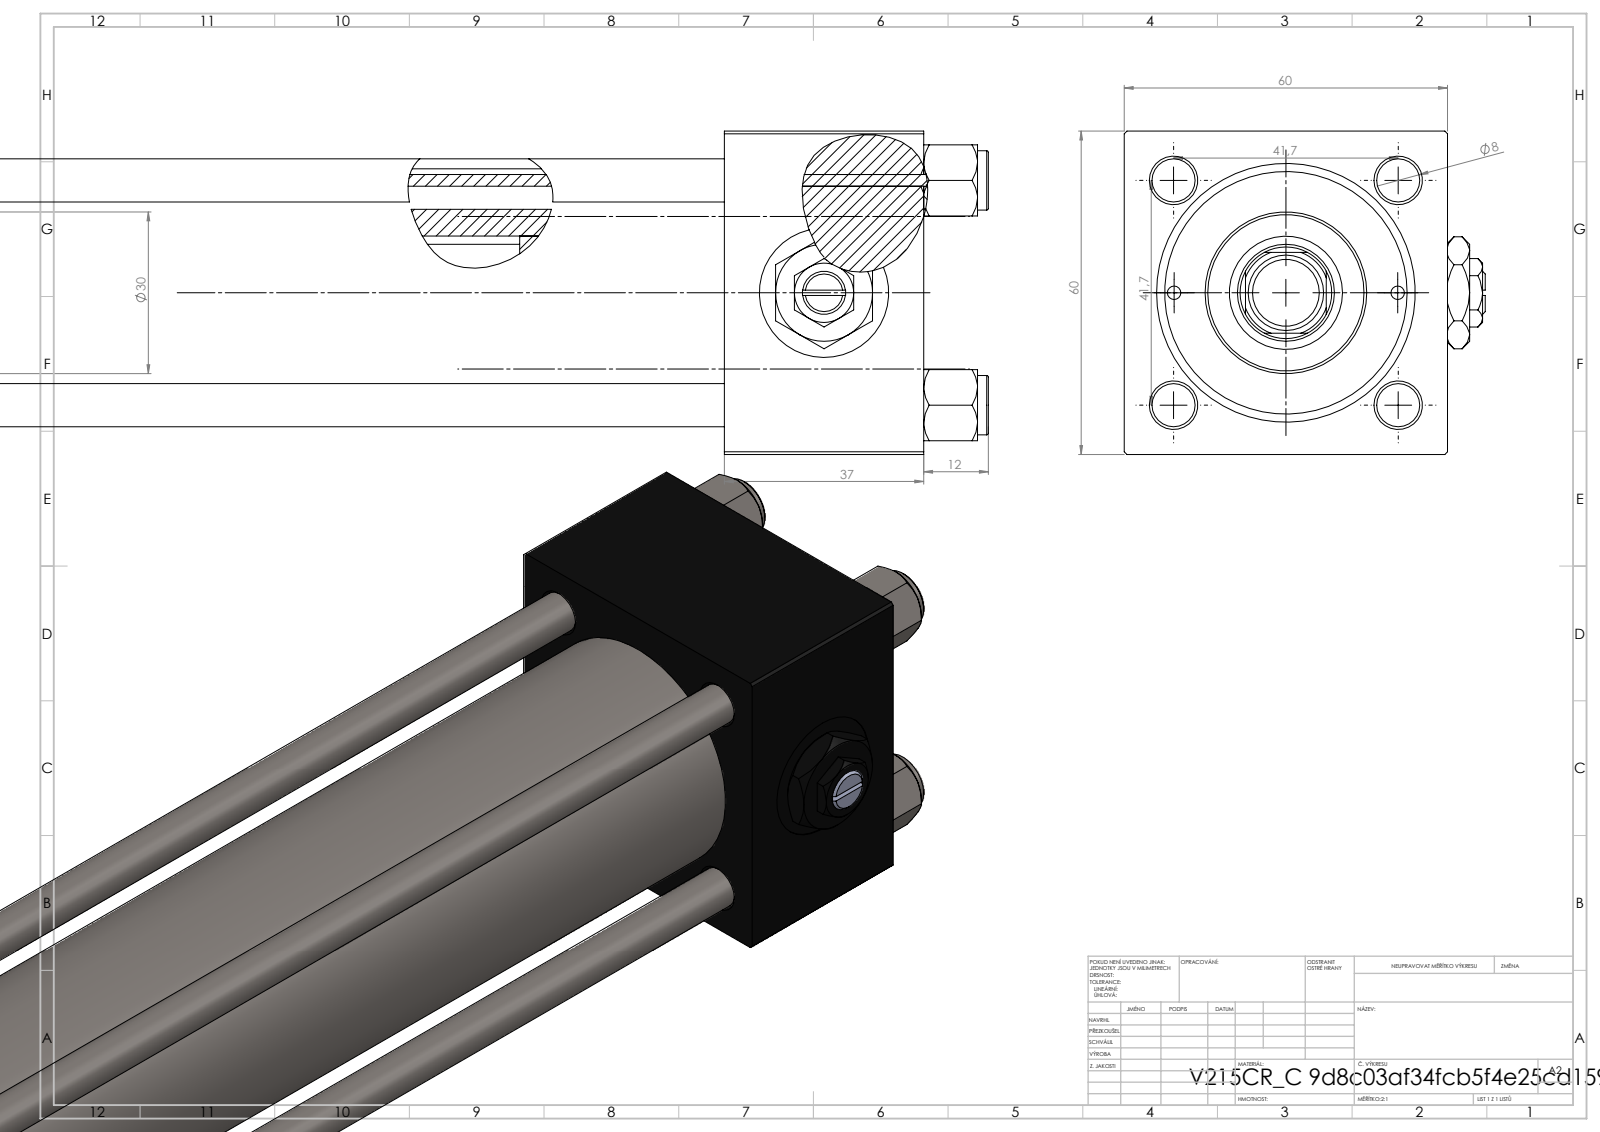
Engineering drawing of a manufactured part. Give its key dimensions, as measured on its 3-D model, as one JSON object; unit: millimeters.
{"part_name": "V215CR_C_TYCINKA; V215CR_C_Body; NUT_M5_C; V215CR_VCP_C (+3 more)", "step_written_by": "SolidWorks 2019 (CONFIG_CONTROL_DESIGN)", "units": "millimeters", "bodies": {"solids": 14, "faces": 1270, "planar": 580, "cylindrical": 106, "other": 584}, "overall_size": [383, 67, 60], "volume_mm3": 556889, "surface_area_mm2": 186359, "round_holes": [[8, 4], [2.5, 2], [7, 2], [16.66, 2], [24, 2], [8.5, 1], [18, 1], [21, 1], [31, 1], [40, 1], [45, 1]], "round_bosses_or_shafts": [[11, 4], [46, 1], [30, 1], [14, 1], [12, 1]], "partial_cylinders_radius": [[8.5, 1]], "face_to_face_distances": [60, 37, 328, 291, 53, 275, 238, 299.3, 262.3, 24.3], "hole_center_spacings": [20.85, 29.49, 41.7, 46.53, 20.75, 58.97, 41.5, 272.5]}
